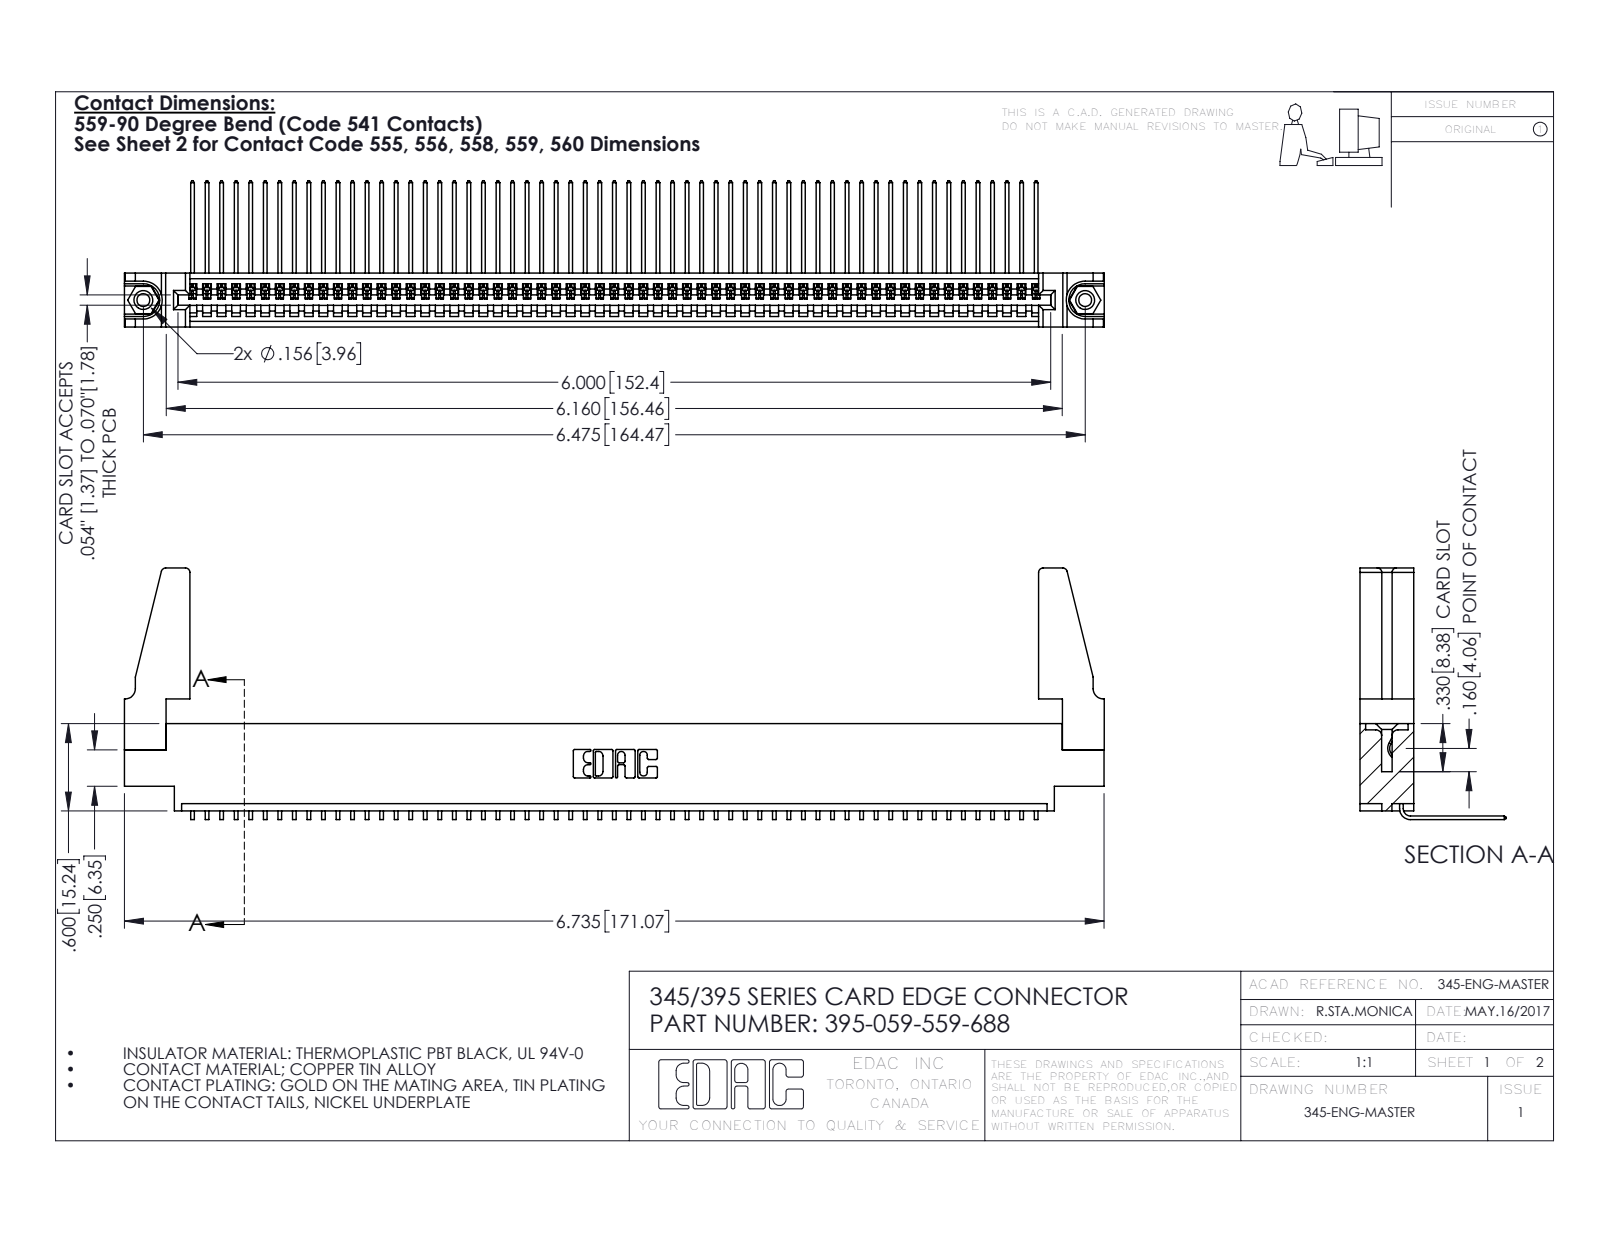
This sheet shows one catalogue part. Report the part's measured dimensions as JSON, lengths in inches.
{"part_name": "395-059-559-688; 345-250-001_345-250-001-102; 345 Part_0.170 Offset - 0.156 Dia-TH; 345-220-078_345-220-088 (+1 more)", "step_written_by": "SolidWorks 2016 (CONFIG_CONTROL_DESIGN)", "units": "inches", "bodies": {"solids": 64, "faces": 3794, "planar": 2634, "cylindrical": 1144, "other": 16}, "overall_size": [6.736, 1.729, 1.005], "volume_in3": 1.204, "surface_area_in2": 41.13, "round_holes": [[0.089, 2], [0.125, 2], [0.156, 2], [0.064, 1]], "round_bosses_or_shafts": [[0.155, 2]], "partial_cylinders_radius": [[0.006, 118], [0.01, 22], [0.03, 8], [0.007, 6], [0.031, 6], [0.026, 3], [0.031, 2], [0.04, 2]], "face_to_face_distances": [0.072, 0.298, 0.37, 0.098, 0.272, 0.025, 0.2, 0.225, 0.175, 0.149], "hole_center_spacings": [0.27, 6.239, 6.475]}
